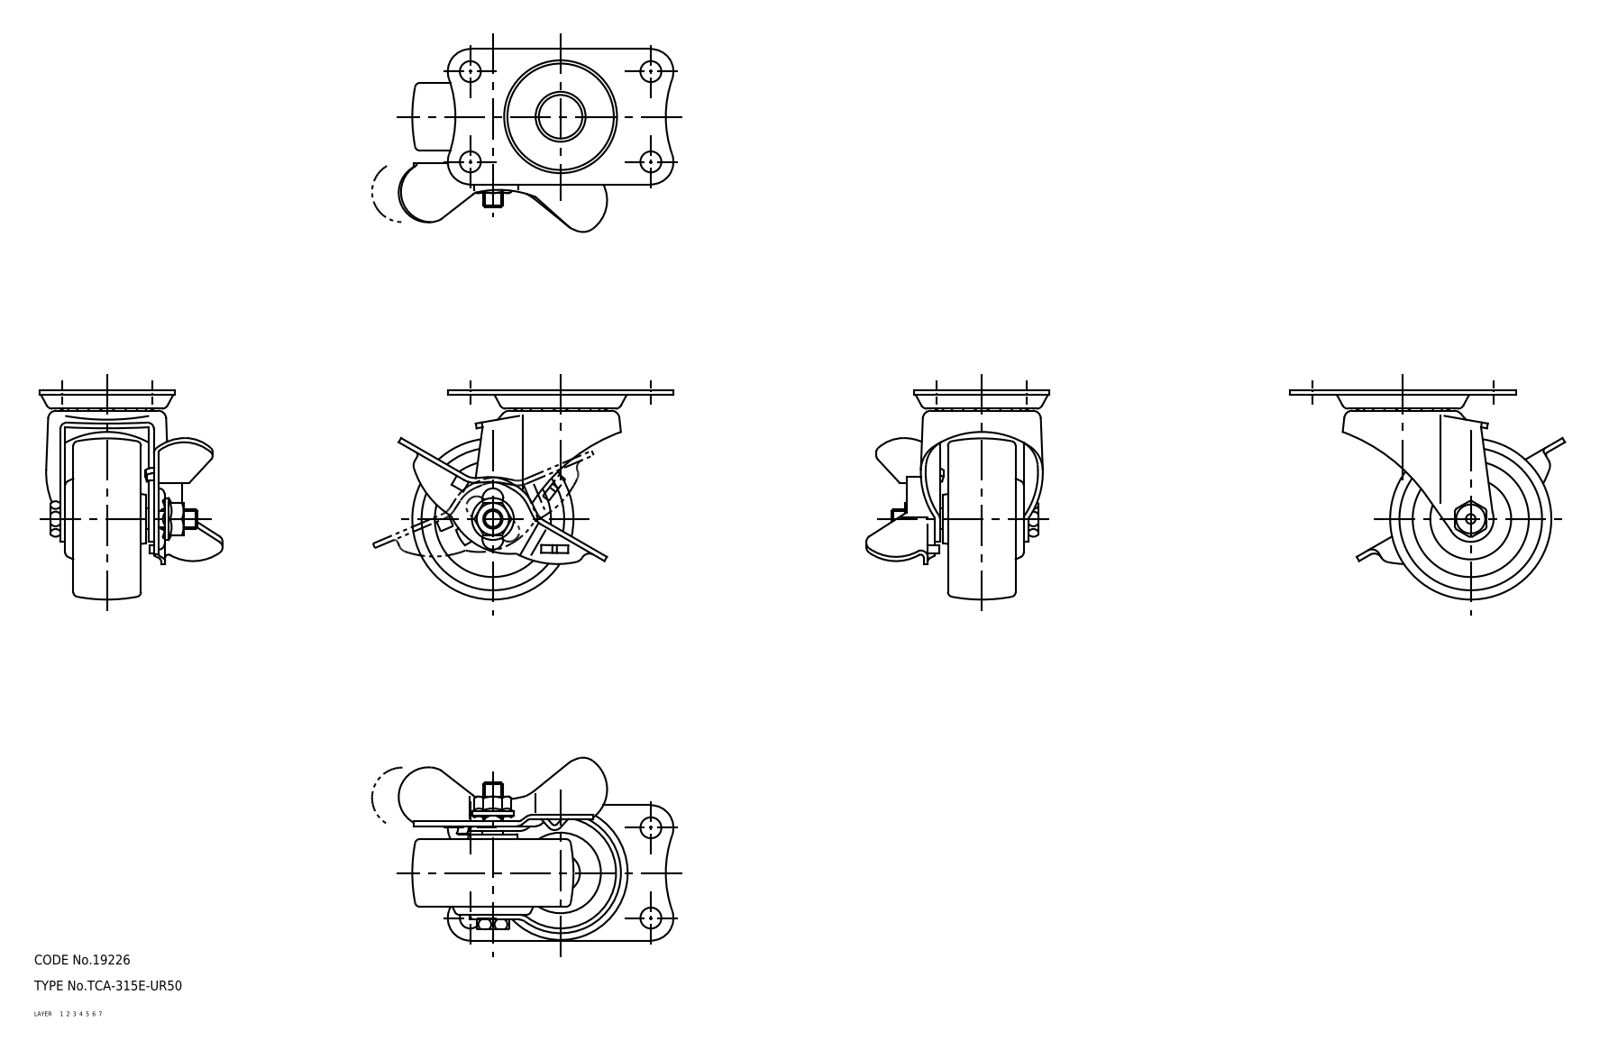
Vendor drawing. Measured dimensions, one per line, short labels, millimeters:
name: wheel; mounting plate; main shaft; lever (+2 more)
written by: CADfix (AUTOMOTIVE_DESIGN)
unit: mm
bodies: 12 solids, 524 faces (0 planar, 0 cylindrical, 524 other)
size: 85.22 × 65 × 56.75
volume: 48 932 mm³; area: 31 161 mm²
